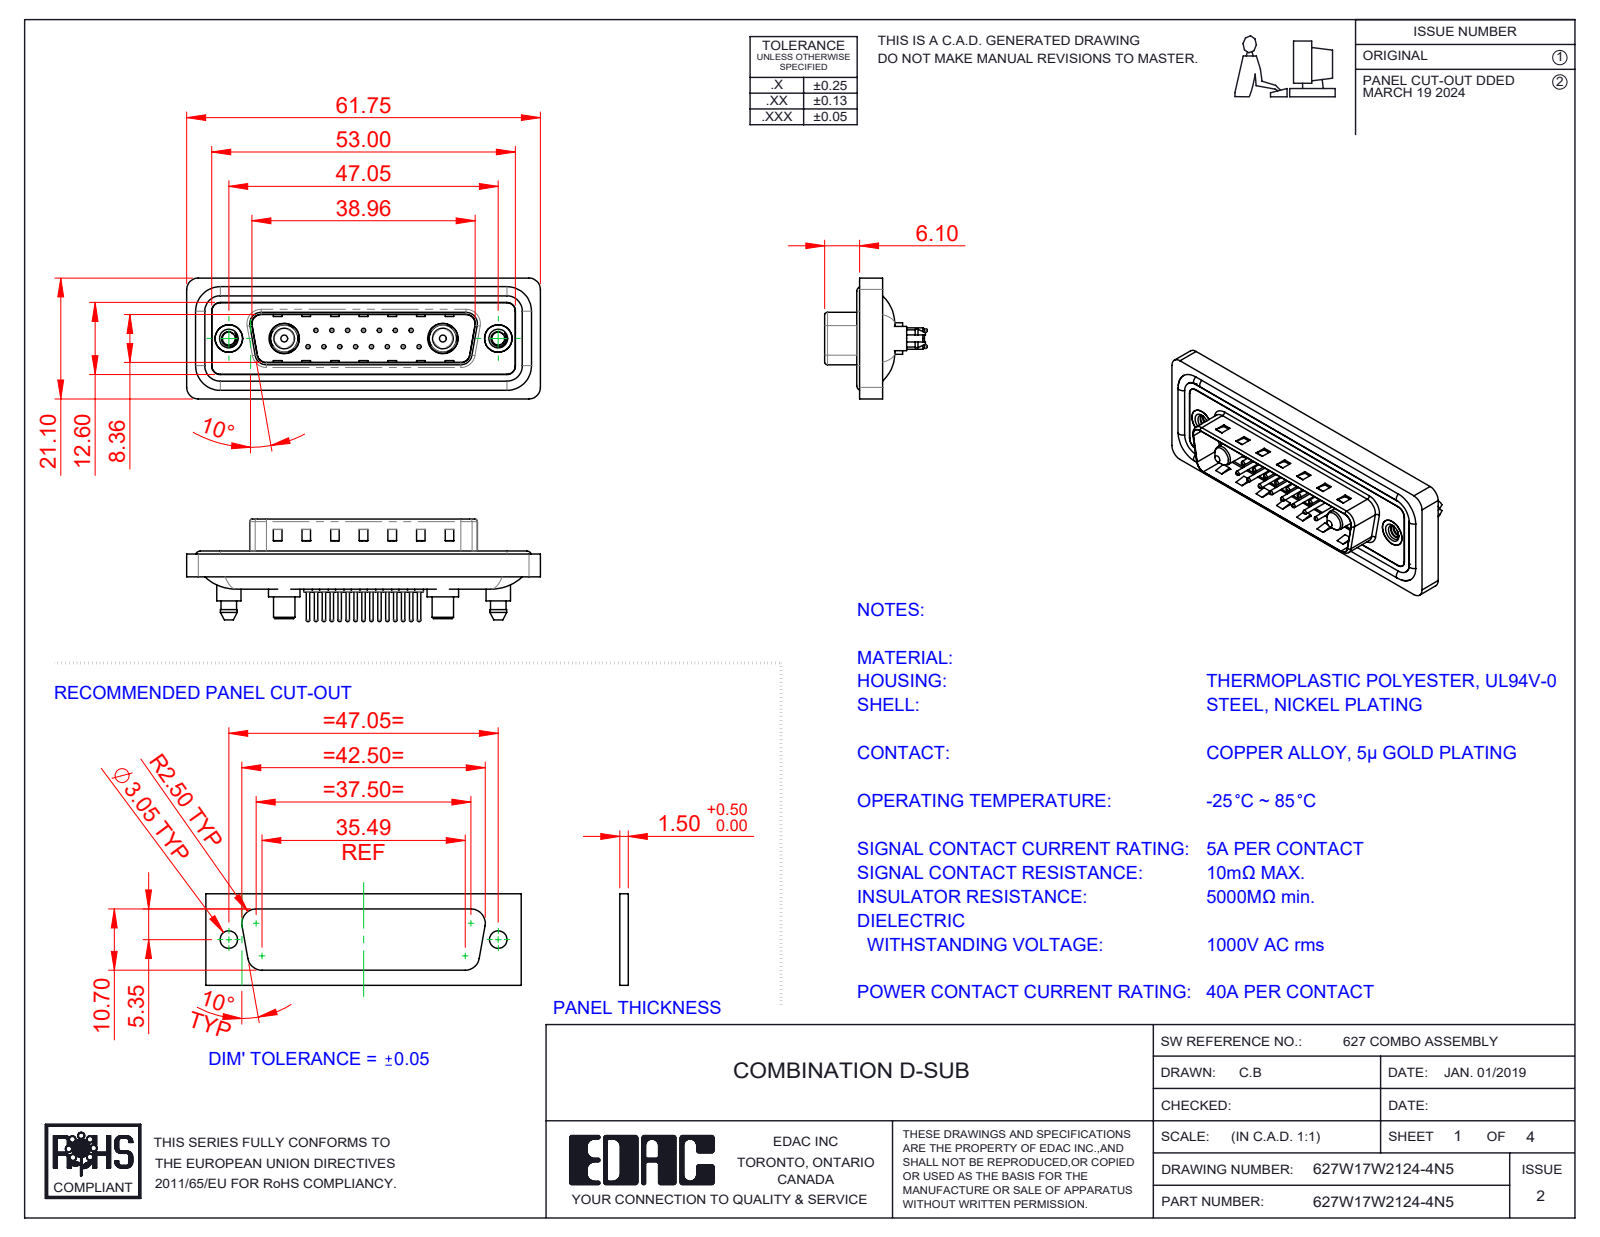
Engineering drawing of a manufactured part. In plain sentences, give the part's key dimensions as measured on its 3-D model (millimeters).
The part is named "627W17W2124-4N5; 627Combo Shell Rear_25 Contacts; 627Combo Shell Front_25 Contacts; 627Combo Contact Row 1_24 (+5 more)". Its 3-D file was written by "SolidWorks 2023 (CONFIG_CONTROL_DESIGN)". It is 26 solids with 1166 faces: 350 planar, 468 cylindrical and 348 other. Overall it measures 61.75 by 21.1 by 17.9 millimeters. Its volume is 7 437 cubic millimeters and its surface area 12 269 square millimeters. Round holes: 15 of diameter 0.75, 15 of diameter 1.6, 15 of diameter 2, 2 of diameter 2.26, 2 of diameter 4, 2 of diameter 4.8, 2 of diameter 4.85, 2 of diameter 5, 2 of diameter 5.3. Round bosses or shafts: 15 of diameter 1.5, 15 of diameter 0.6, 4 of diameter 1.6, 2 of diameter 5.5, 2 of diameter 5.4, 2 of diameter 5.2, 2 of diameter 4.9, 2 of diameter 4.75. Partial cylindrical surfaces (rounded edges, fillets, slot ends): 24 of radius 1.5, 18 of radius 2, 10 of radius 1.6, 8 of radius 0.5, 4 of radius 0.25, 4 of radius 0.6, 4 of radius 0.65, 4 of radius 0.9. The main face-to-face distances are 0.4, 1.5, 1.1, 1.6, 0.5, 3.1, 2.9, 0.82, 9.58, 4.1. The hole center spacings are 3.16, 2.77, 5.54, 8.31, 5.04, 7.49, 11.08, 5.03.
